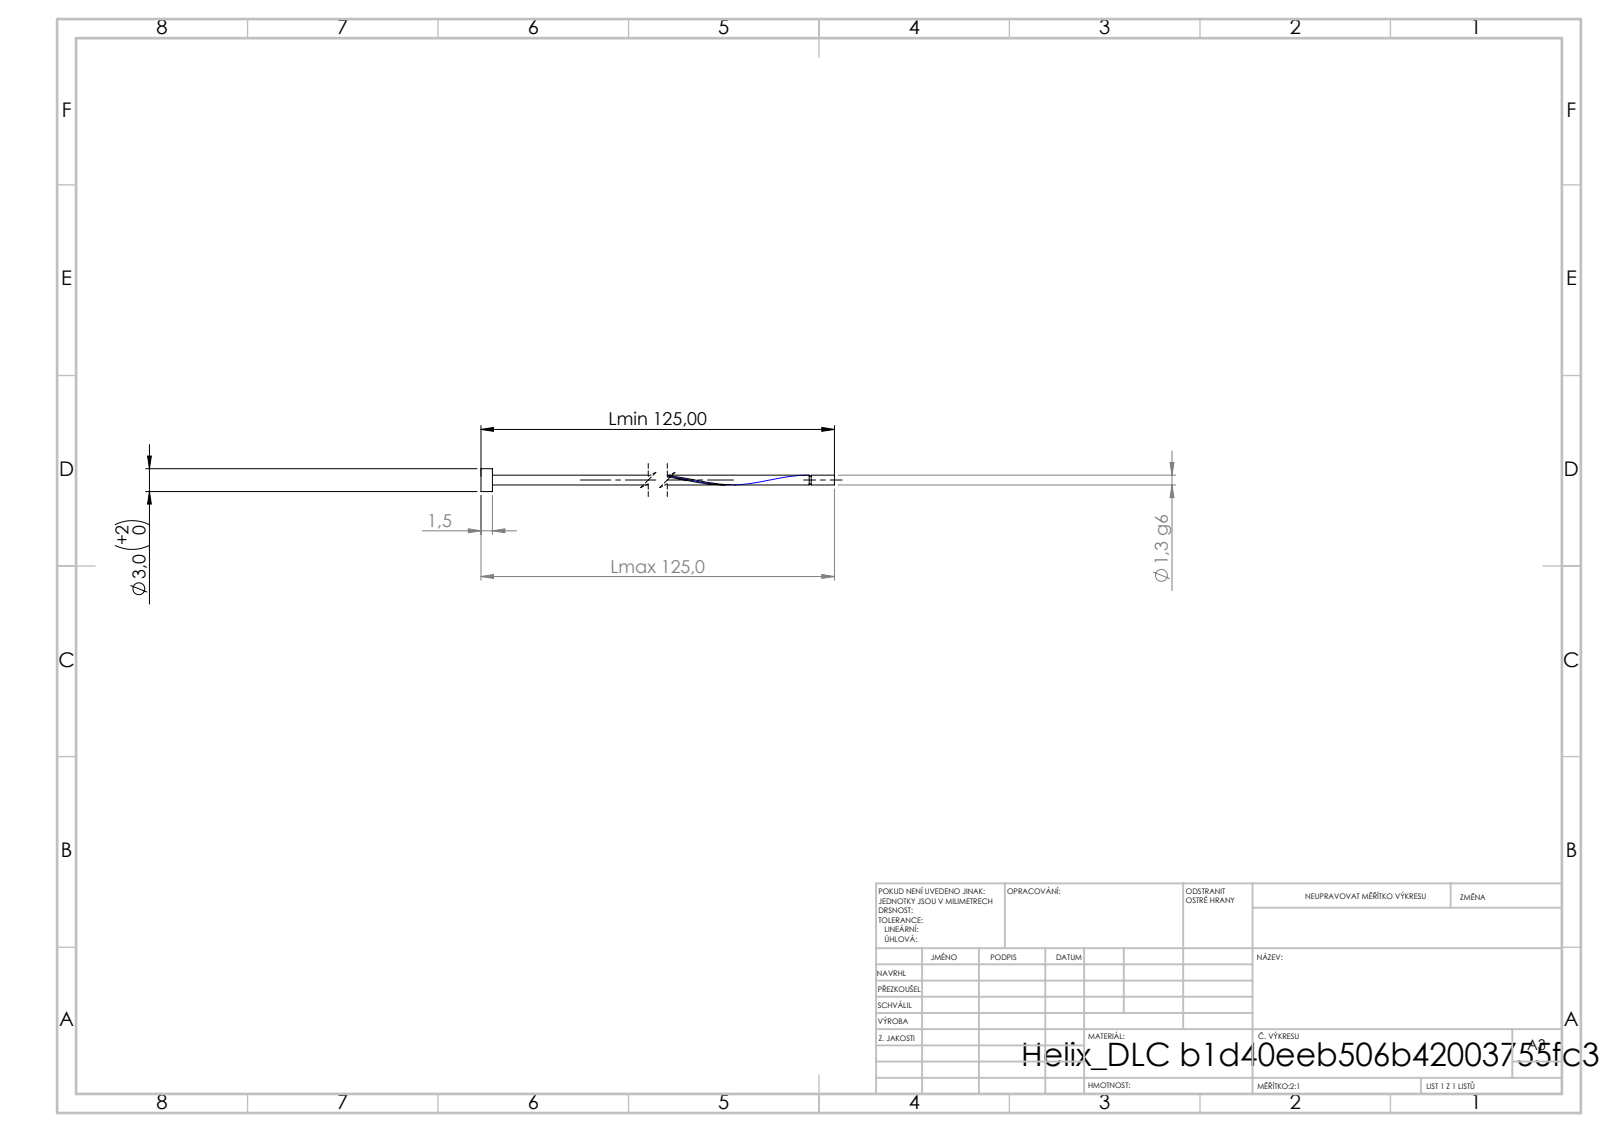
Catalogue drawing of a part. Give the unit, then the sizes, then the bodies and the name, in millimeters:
Units: millimetres
Overall size (bounding box): 125 × 3 × 3
Round bosses / shafts (diameter × count): ⌀3 ×1, ⌀1.3 ×1, ⌀1.04 ×1
Main face-to-face distances: 1.5, 125, 123.5, 121.94, 120.44, 3.06, 121.68, 120.18, 3.32, 59.18
Volume: 210 mm³ · Surface area: 712 mm²
Bodies: 1 solid, 16 faces (6 planar, 9 cylindrical, 1 other)
STEP written by: SolidWorks 2019 (CONFIG_CONTROL_DESIGN)
